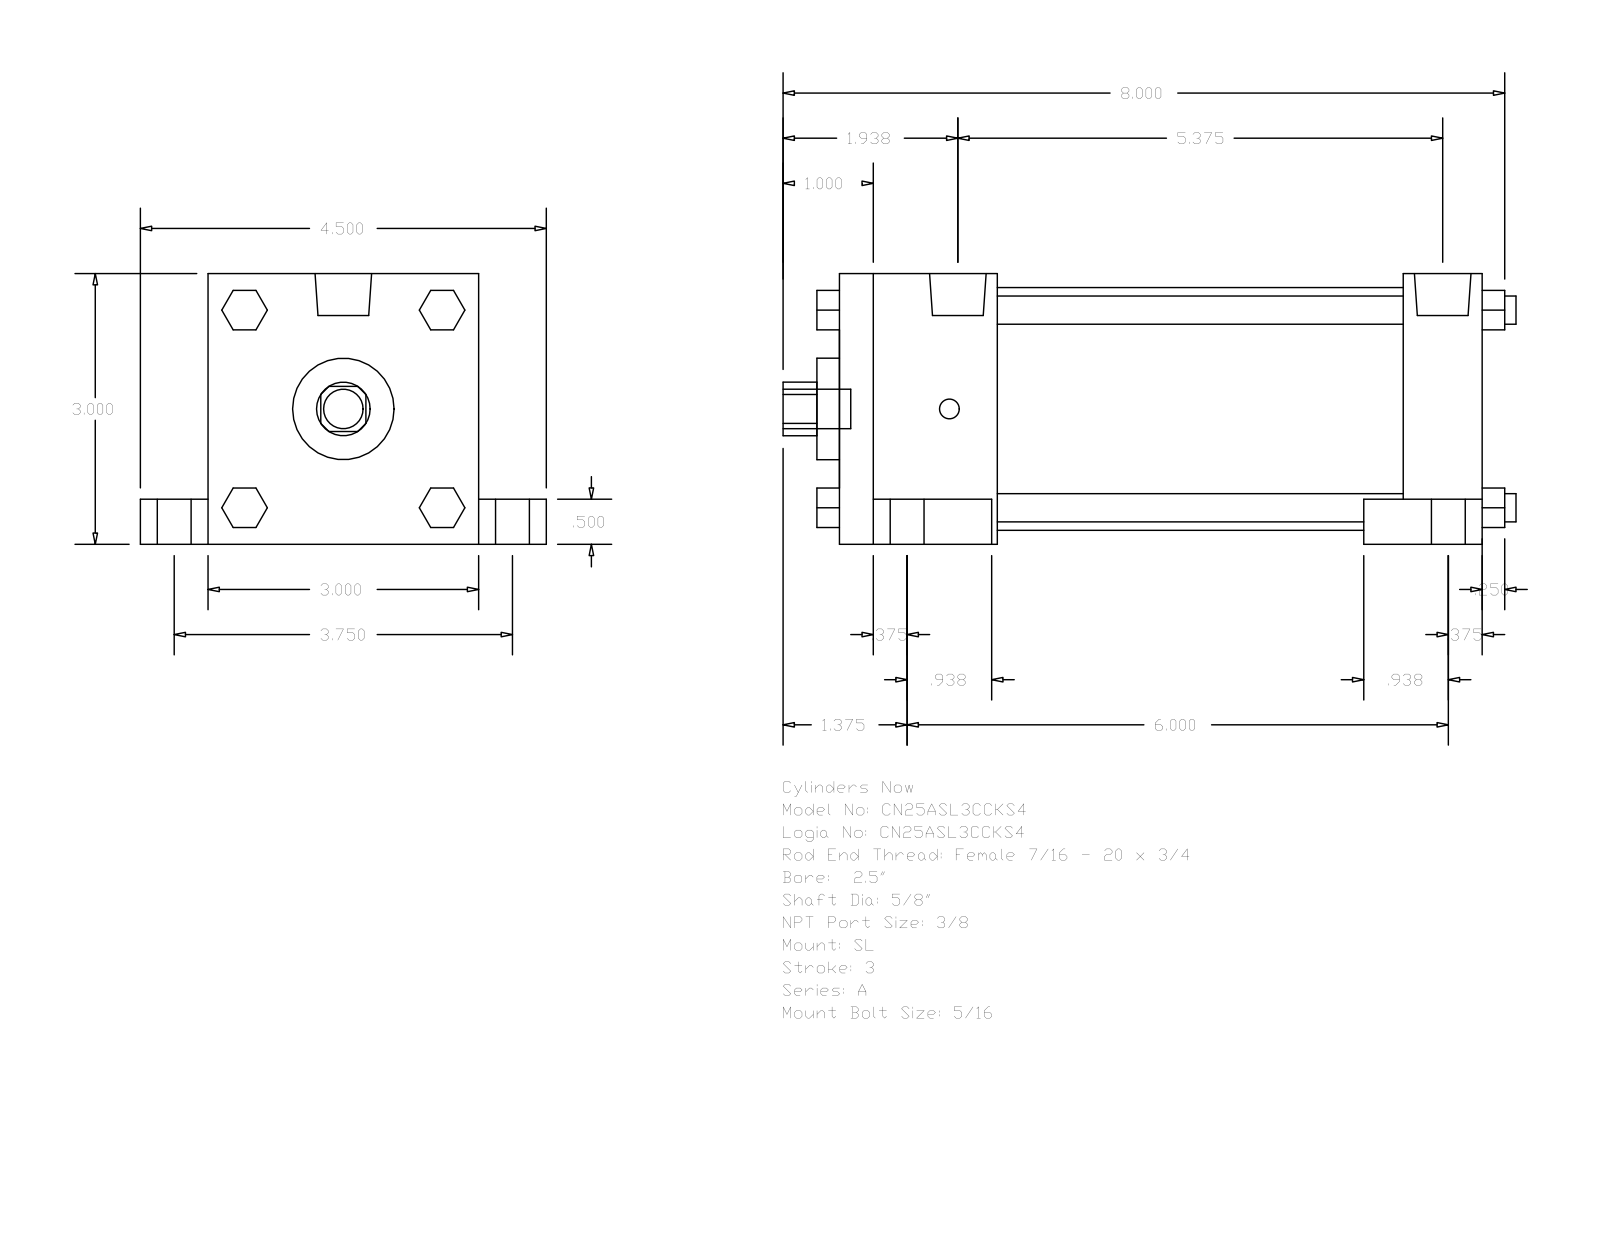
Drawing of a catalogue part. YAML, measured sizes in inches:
part_name: "A_SL__0250_0.625"
step_written_by: "GSSL Pune (CONFIG_CONTROL_DESIGN)"
units: inches
bodies: {solids: 0, faces: 148, planar: 112, cylindrical: 36, other: 0}
overall_size: [8.125, 4.5, 3]
round_holes:
  - {diameter: 0.625, count: 1}
  - {diameter: 1.125, count: 1}
  - {diameter: 2.69, count: 1}
round_bosses_or_shafts:
  - {diameter: 0.625, count: 4}
  - {diameter: 0.375, count: 4}
  - {diameter: 0.313, count: 4}
  - {diameter: 0.219, count: 4}
  - {diameter: 0.627, count: 2}
  - {diameter: 0.437, count: 1}
partial_cylinders:
  - {radius: 0.297, count: 1}
face_to_face_distances: [3, 7.125, 1.75, 5.375, 6.25, 4.5, 0.875, 0.5, 2.5, 0.75]
